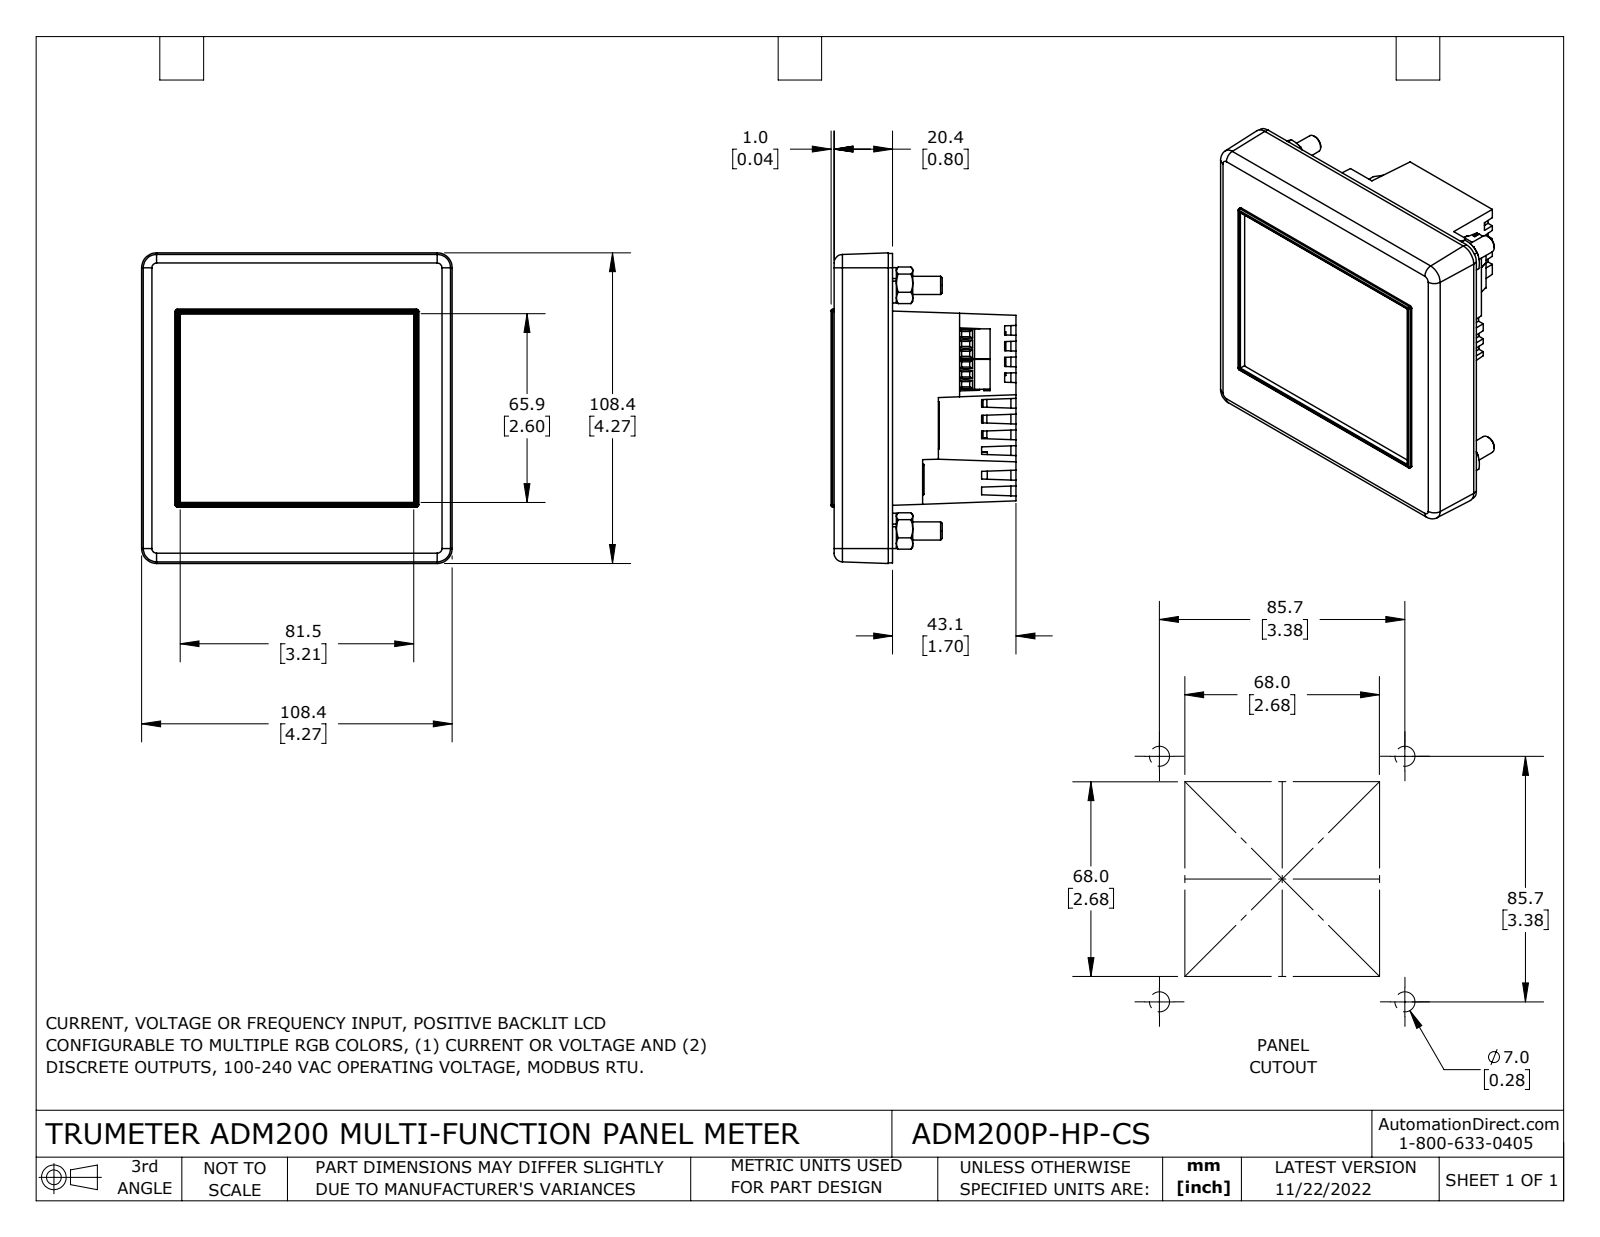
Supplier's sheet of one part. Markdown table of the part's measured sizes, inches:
| quantity | value |
| --- | --- |
| part name | ADM200P-HP-CS |
| STEP written by | SolidWorks 2021 (CONFIG_CONTROL_DESIGN) |
| units | inches |
| bodies | 23 solids, 2059 faces (1384 planar, 290 cylindrical, 385 other) |
| overall size | 4.269 × 4.269 × 2.541 |
| volume | 7.808 in³ |
| surface area | 190.8 in² |
| round holes (diameter × count) | 0.071 × 9, 0.114 × 6, 0.118 × 5, 0.213 × 4, 0.25 × 4, 0.26 × 4, 0.295 × 4, 0.154 × 2 |
| round bosses / shafts (diameter × count) | 0.039 × 5, 0.487 × 4, 0.438 × 4, 0.024 × 4, 0.079 × 2 |
| partial cylindrical surfaces (radius × count) | 0.006 × 32, 0.02 × 30, 0.039 × 7, 0.016 × 4, 0.03 × 4, 0.118 × 4, 0.197 × 4, 0.004 × 2 |
| main face-to-face distances | 0.031, 0.635, 0.11, 0.073, 0.059, 0.079, 0.694, 3.395, 3.468, 0.047 |
| hole center spacings | 0.709, 3.228, 0.136, 0.293, 0.986, 1.417, 2.126, 2.399 |
